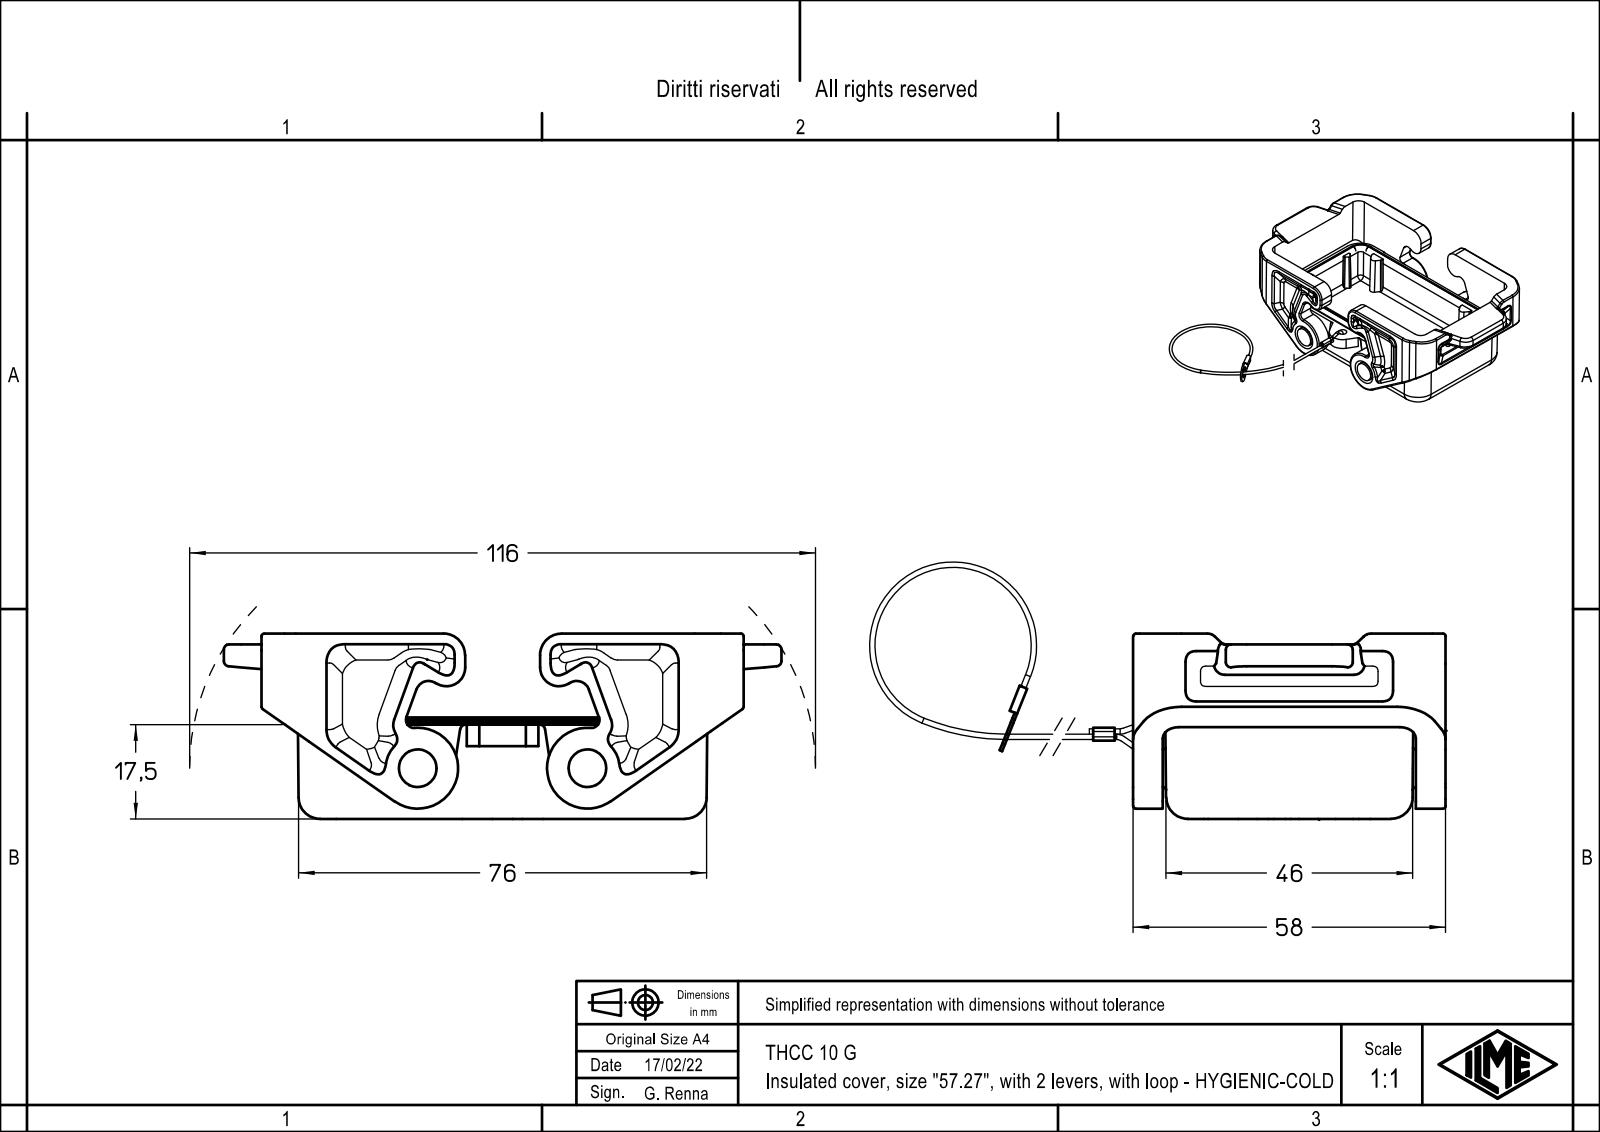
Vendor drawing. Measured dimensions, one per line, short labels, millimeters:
name: Coperchietto_10p_leve
written by: Creo Elements/Direct Modeling 20.1B 02-Apr-2019 (C) Parametric Technology GmbH (AUTOMOTIVE_DESIGN)
unit: mm
bodies: 1 solid, 601 faces (214 planar, 300 cylindrical, 87 other)
size: 227.87 × 103.5 × 34.55
volume: 58 291 mm³; area: 31 473 mm²
holes: 1× ⌀3, 1× ⌀4.2
bosses: 5× ⌀1, 3× ⌀7
rounds: 44× R0.15, 40× R1, 18× R1.5, 16× R1.3, 16× R3, 13× R0.5, 12× R2, 10× R4
face distances: 5.5, 52.5, 47, 34.4, 28.9, 58, 12, 79.5, 17.5, 16.9
